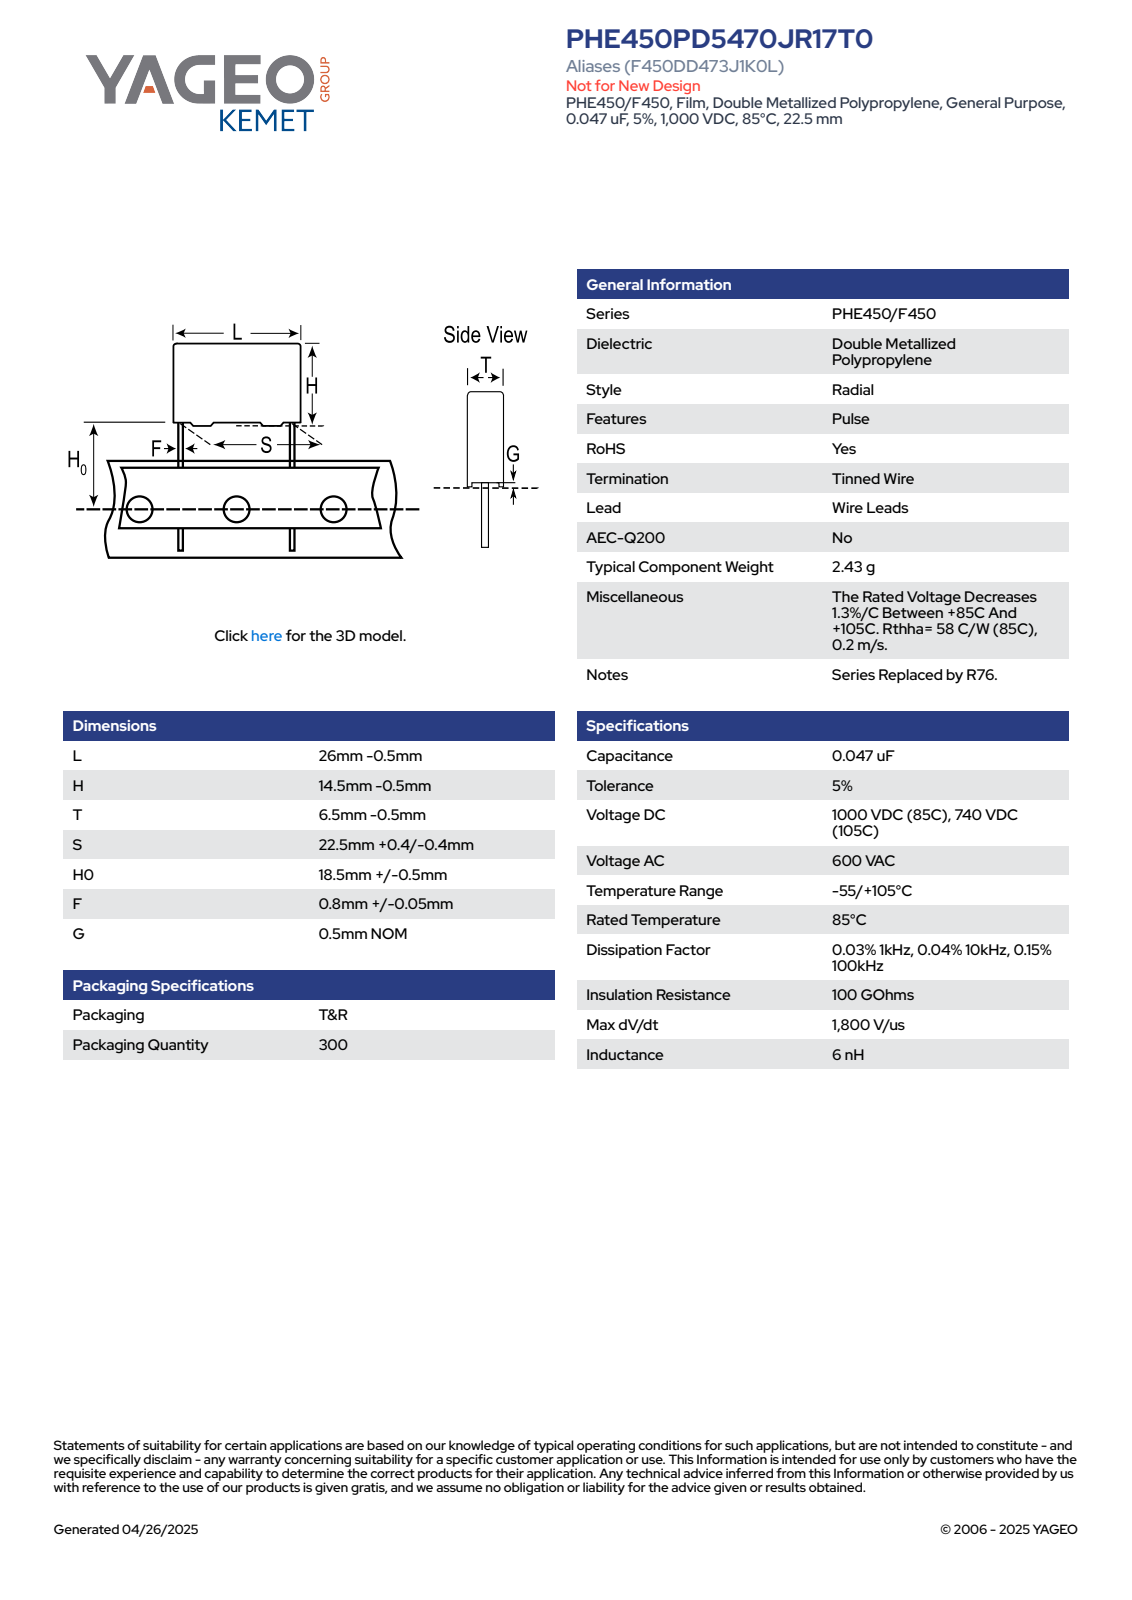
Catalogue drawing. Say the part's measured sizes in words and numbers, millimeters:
The part is named "CFR_RBG_26X14.5X6.5_L25.5H14T6S22.5H019F0.85G0.5". Its 3-D file was written by "SolidWorks 2014 (AUTOMOTIVE_DESIGN)". It is 4 solids with 89 faces: 81 planar, 8 cylindrical and 0 other. Overall it measures 33 by 25.5 by 6 millimeters. Its volume is 2 087 cubic millimeters and its surface area 1 334 square millimeters. Round bosses or shafts: 2 of diameter 0.85. Partial cylindrical surfaces (rounded edges, fillets, slot ends): 4 of radius 0.5. The main face-to-face distances are 6, 13.5, 25.5, 0.34, 5.66, 0.5, 14, 5.32, 19, 19.5.
